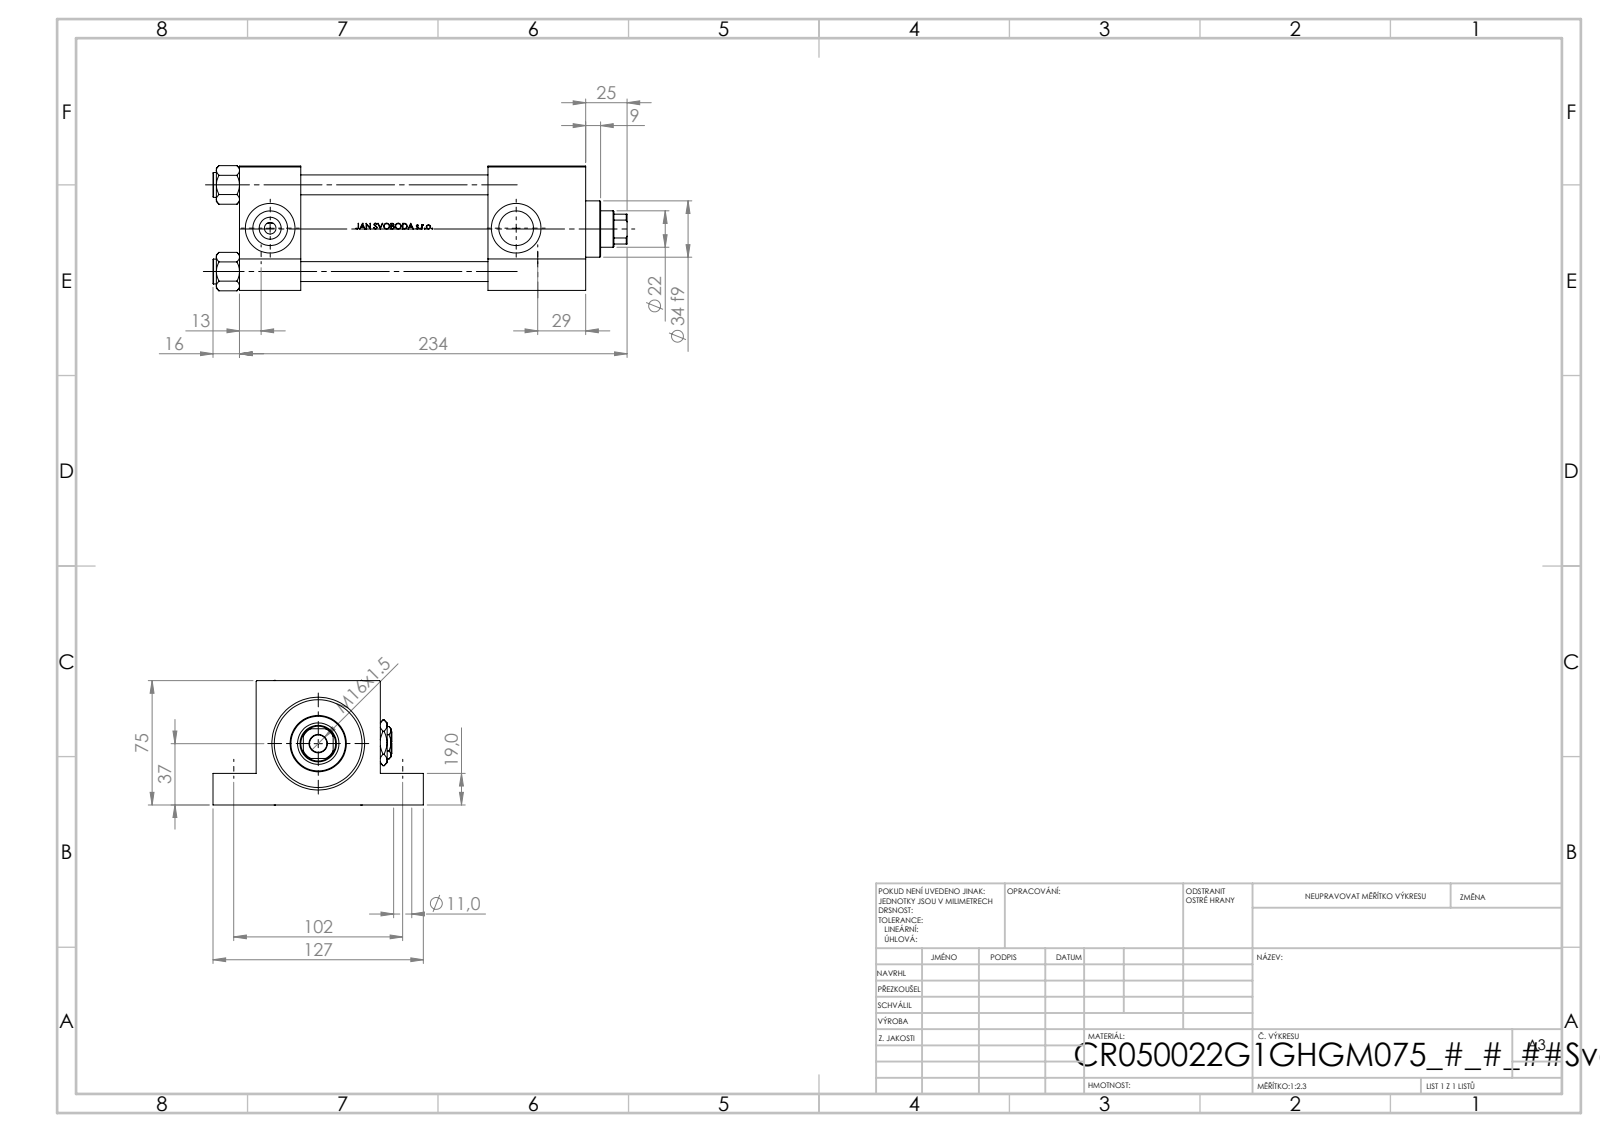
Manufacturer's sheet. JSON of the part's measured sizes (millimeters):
{"part_name": "Zatka_pro_OIL_PORT; V215CR_G_Body; V215CR_VCP_G; NUT_M5_G (+2 more)", "step_written_by": "SolidWorks 2019 (CONFIG_CONTROL_DESIGN)", "units": "millimeters", "bodies": {"solids": 12, "faces": 1134, "planar": 454, "cylindrical": 128, "other": 552}, "overall_size": [250, 127, 75.54], "volume_mm3": 825665, "surface_area_mm2": 191714, "round_holes": [[11, 4], [12, 4], [7, 2], [20.96, 2], [30, 2], [10.5, 1], [22, 1], [25, 1], [41, 1], [50, 1], [53, 1]], "round_bosses_or_shafts": [[15, 4], [56, 1], [34, 1]], "partial_cylinders_radius": [[10.5, 1]], "face_to_face_distances": [75, 37, 209, 172, 19, 56, 150, 113, 59, 26], "hole_center_spacings": [52.3, 36.63, 37.34, 73.96, 102, 167, 195.69, 148.5]}
